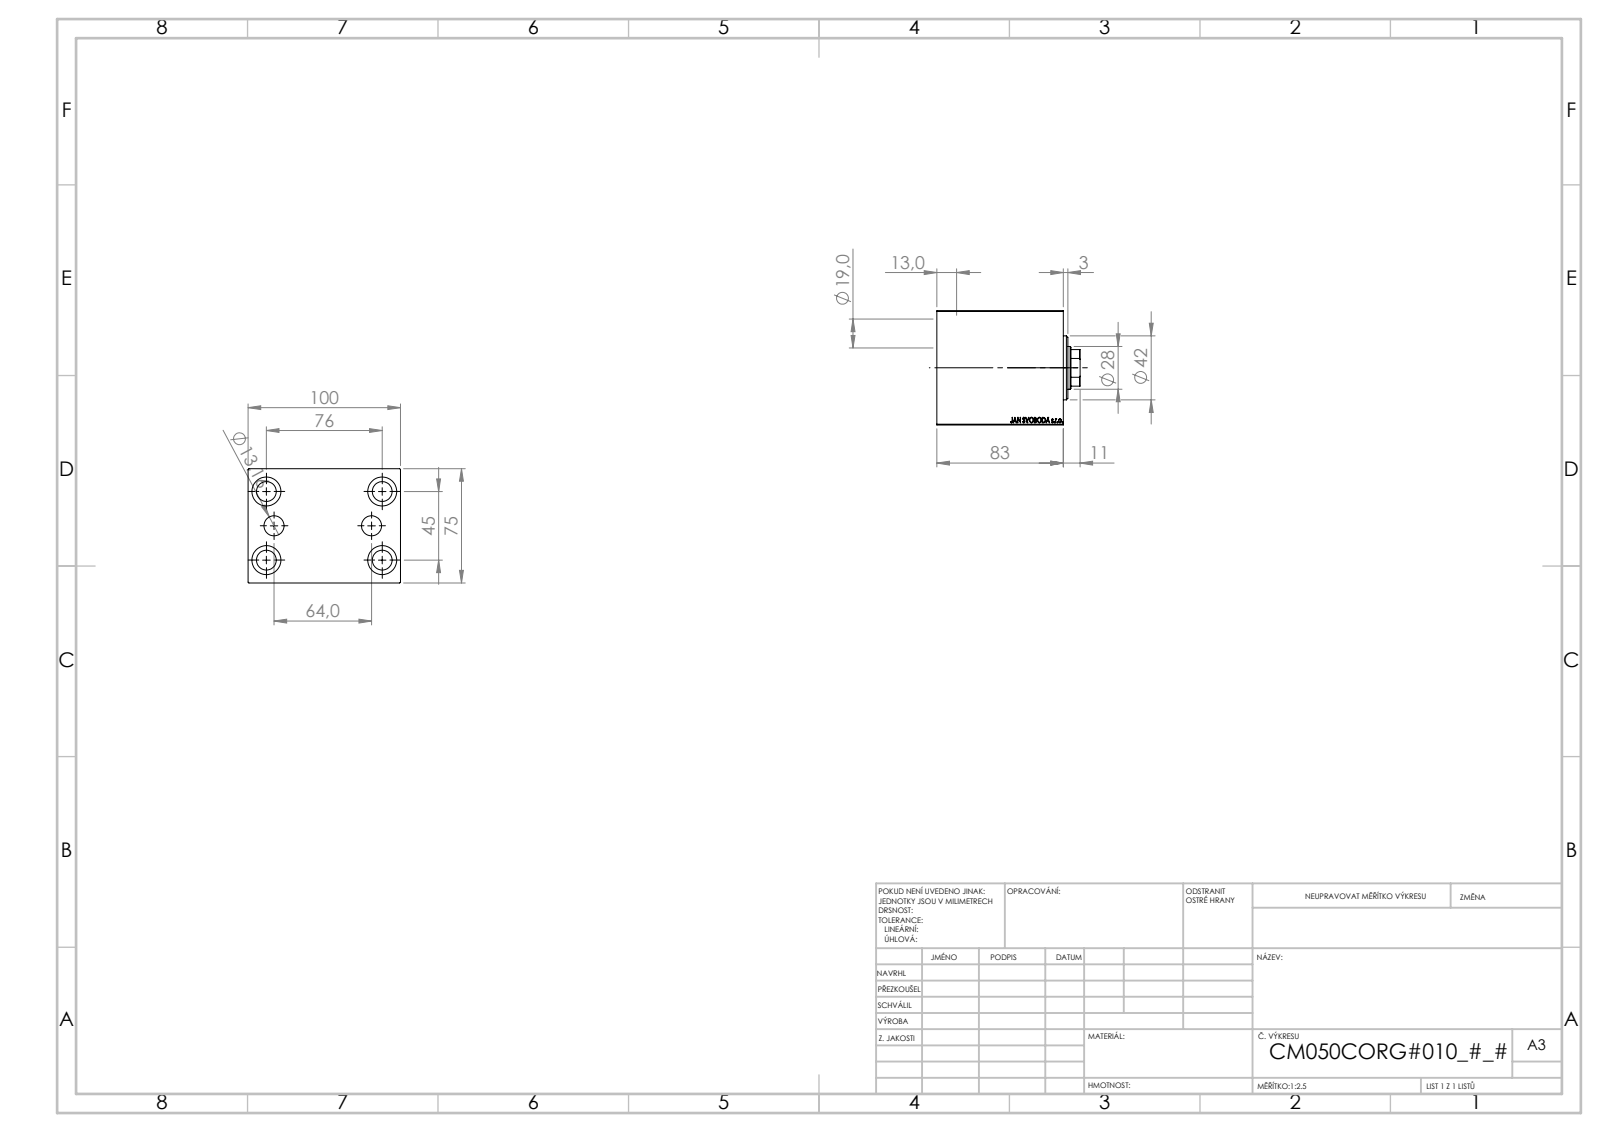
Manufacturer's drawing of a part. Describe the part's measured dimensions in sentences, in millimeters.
The part is named "V450CM_VC_B; V450CM_C_VCP; V450CM_C_Body". Its 3-D file was written by "SolidWorks 2019 (CONFIG_CONTROL_DESIGN)". It is 3 solids with 855 faces: 407 planar, 54 cylindrical and 394 other. Overall it measures 100 by 94 by 75 millimeters. Its volume is 547 377 cubic millimeters and its surface area 89 632 square millimeters. Round holes: 4 of diameter 13, 4 of diameter 19, 2 of diameter 13.16, 1 of diameter 18.5, 1 of diameter 28, 1 of diameter 31.5, 1 of diameter 50, 1 of diameter 52, 1 of diameter 57. Round bosses or shafts: 1 of diameter 42. Partial cylindrical surfaces (rounded edges, fillets, slot ends): 1 of radius 13.5. The main face-to-face distances are 75, 100, 83, 51, 32, 10, 21.6, 29.4, 61.4, 51.4. The hole center spacings are 44.16, 23.05, 23.56, 45, 72.58, 74.48, 76, 88.32.
